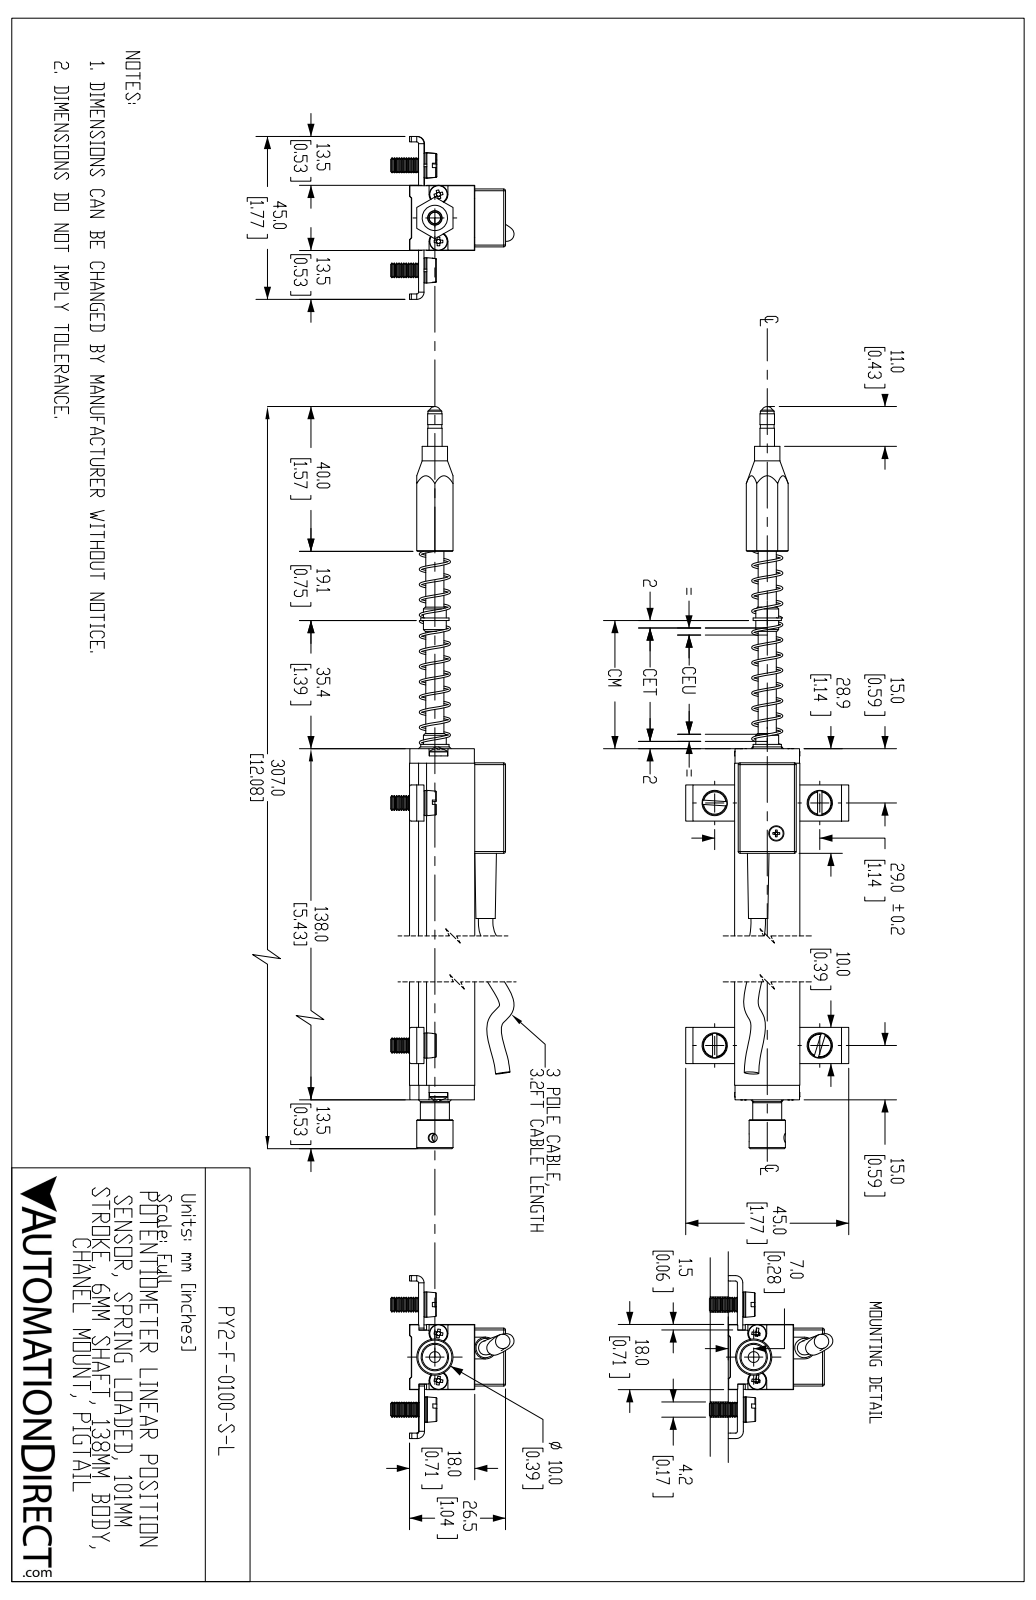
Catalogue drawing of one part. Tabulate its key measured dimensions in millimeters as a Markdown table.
| quantity | value |
| --- | --- |
| part name | PY2-F-0100-S-L |
| STEP written by | SolidWorks 2019 (AUTOMOTIVE_DESIGN) |
| units | millimeters |
| bodies | 37 solids, 1003 faces (341 planar, 257 cylindrical, 405 other) |
| overall size | 307 × 45 × 34 |
| volume | 55 210 mm³ |
| surface area | 31 520 mm² |
| round holes (diameter × count) | 3.6 × 4, 4.3 × 4, 2.3 × 2, 2.5 × 2, 2.7 × 2, 6 × 2, 1.6 × 1, 2 × 1, 2.1 × 1, 2.6 × 1, 4 × 1, 4.2 × 1 |
| round bosses / shafts (diameter × count) | 4 × 6, 7 × 4, 5 × 3, 2.5 × 3, 3.8 × 2, 10 × 1, 8 × 1, 7.8 × 1 |
| partial cylindrical surfaces (radius × count) | 0.5 × 25, 2 × 4, 2.6 × 2, 4.5 × 1 |
| main face-to-face distances | 18, 1.5, 0.5, 17.5, 2, 15.5, 16.5, 4, 2.5, 1 |
| hole center spacings | 6.6, 14.6, 29, 108, 110.6, 111.8, 10.3, 13 |
